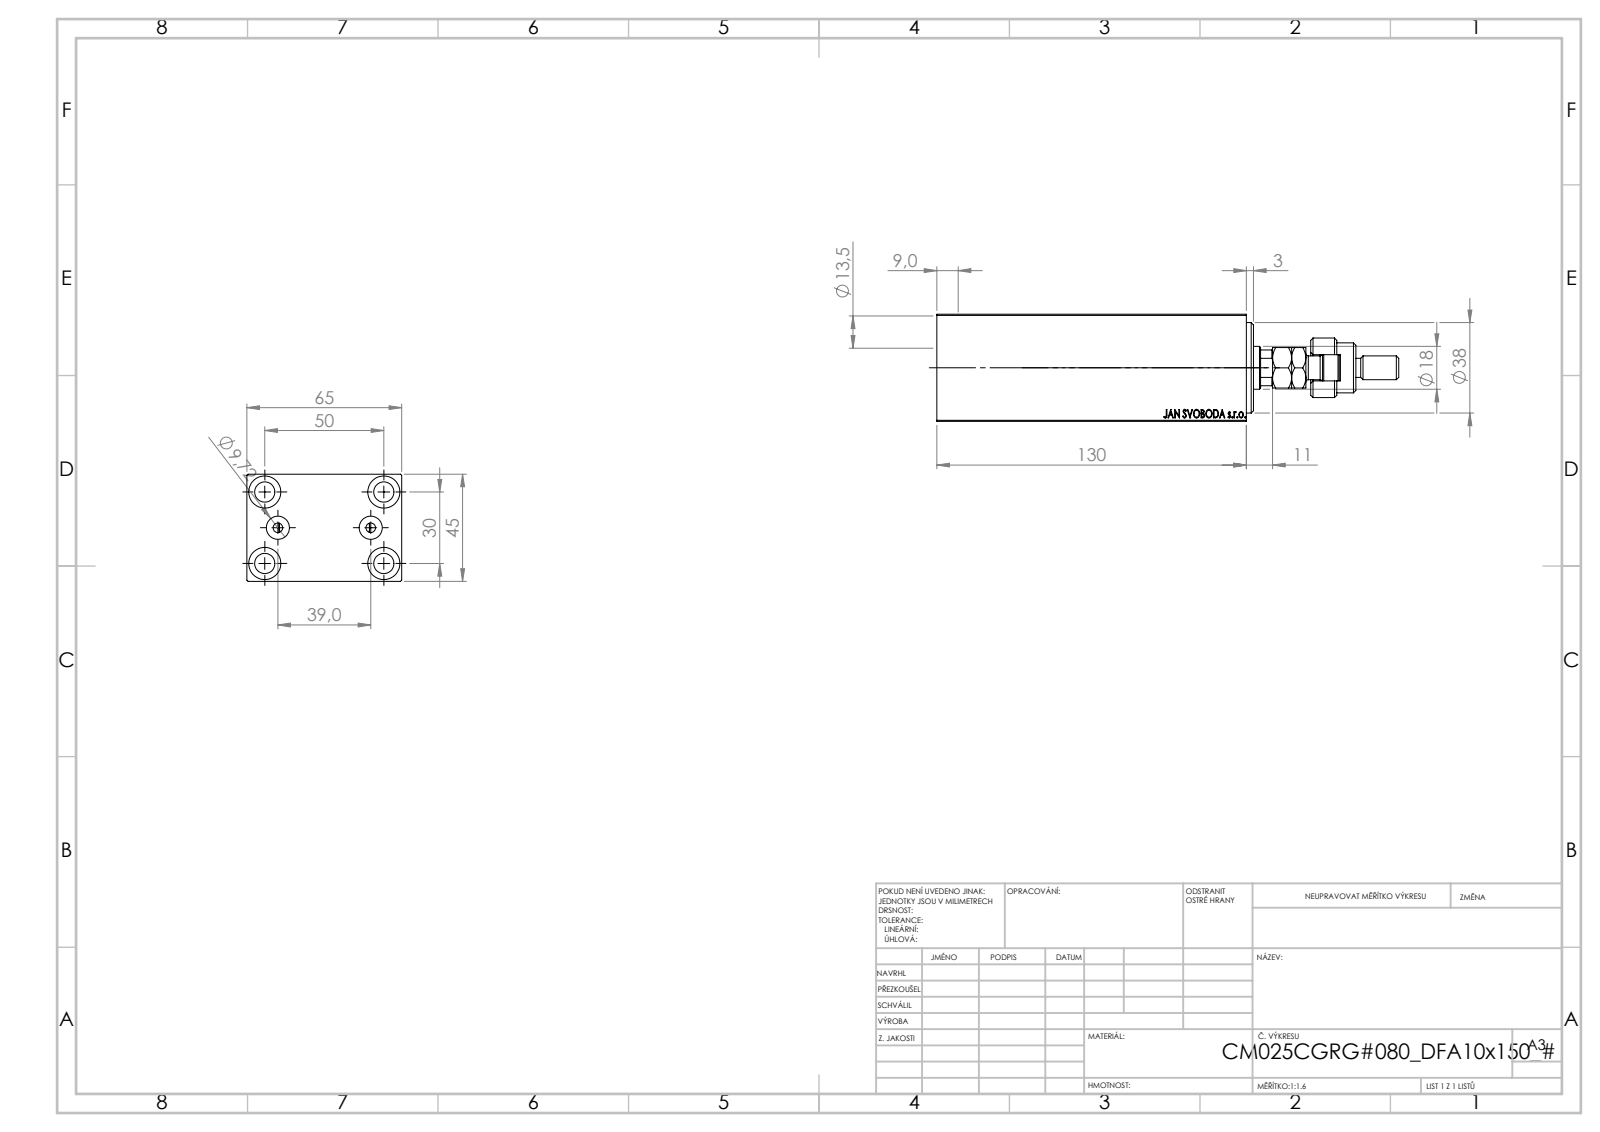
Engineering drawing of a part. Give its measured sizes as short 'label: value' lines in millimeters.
name: MFA; V450CM_VC_B; V450CM_C_Body; V450CM_C_VCP (+1 more)
written by: SolidWorks 2019 (CONFIG_CONTROL_DESIGN)
unit: mm
bodies: 5 solids, 943 faces (436 planar, 69 cylindrical, 438 other)
size: 194 × 65 × 45
volume: 336 945 mm³; area: 83 100 mm²
holes: 5× ⌀8.5, 4× ⌀13.5, 2× ⌀4, 2× ⌀9.72, 1× ⌀18, 1× ⌀21.5, 1× ⌀27, 1× ⌀38
bosses: 1× ⌀25, 1× ⌀21, 1× ⌀16, 1× ⌀10, 1× ⌀8
rounds: 1× R5.5, 1× R8.5, 1× R8.75
face distances: 45, 65, 124, 5, 3, 125, 130, 8, 6, 119
hole spacings: 15.98, 29.15, 46.96, 19.5, 30, 50, 58.31, 39
